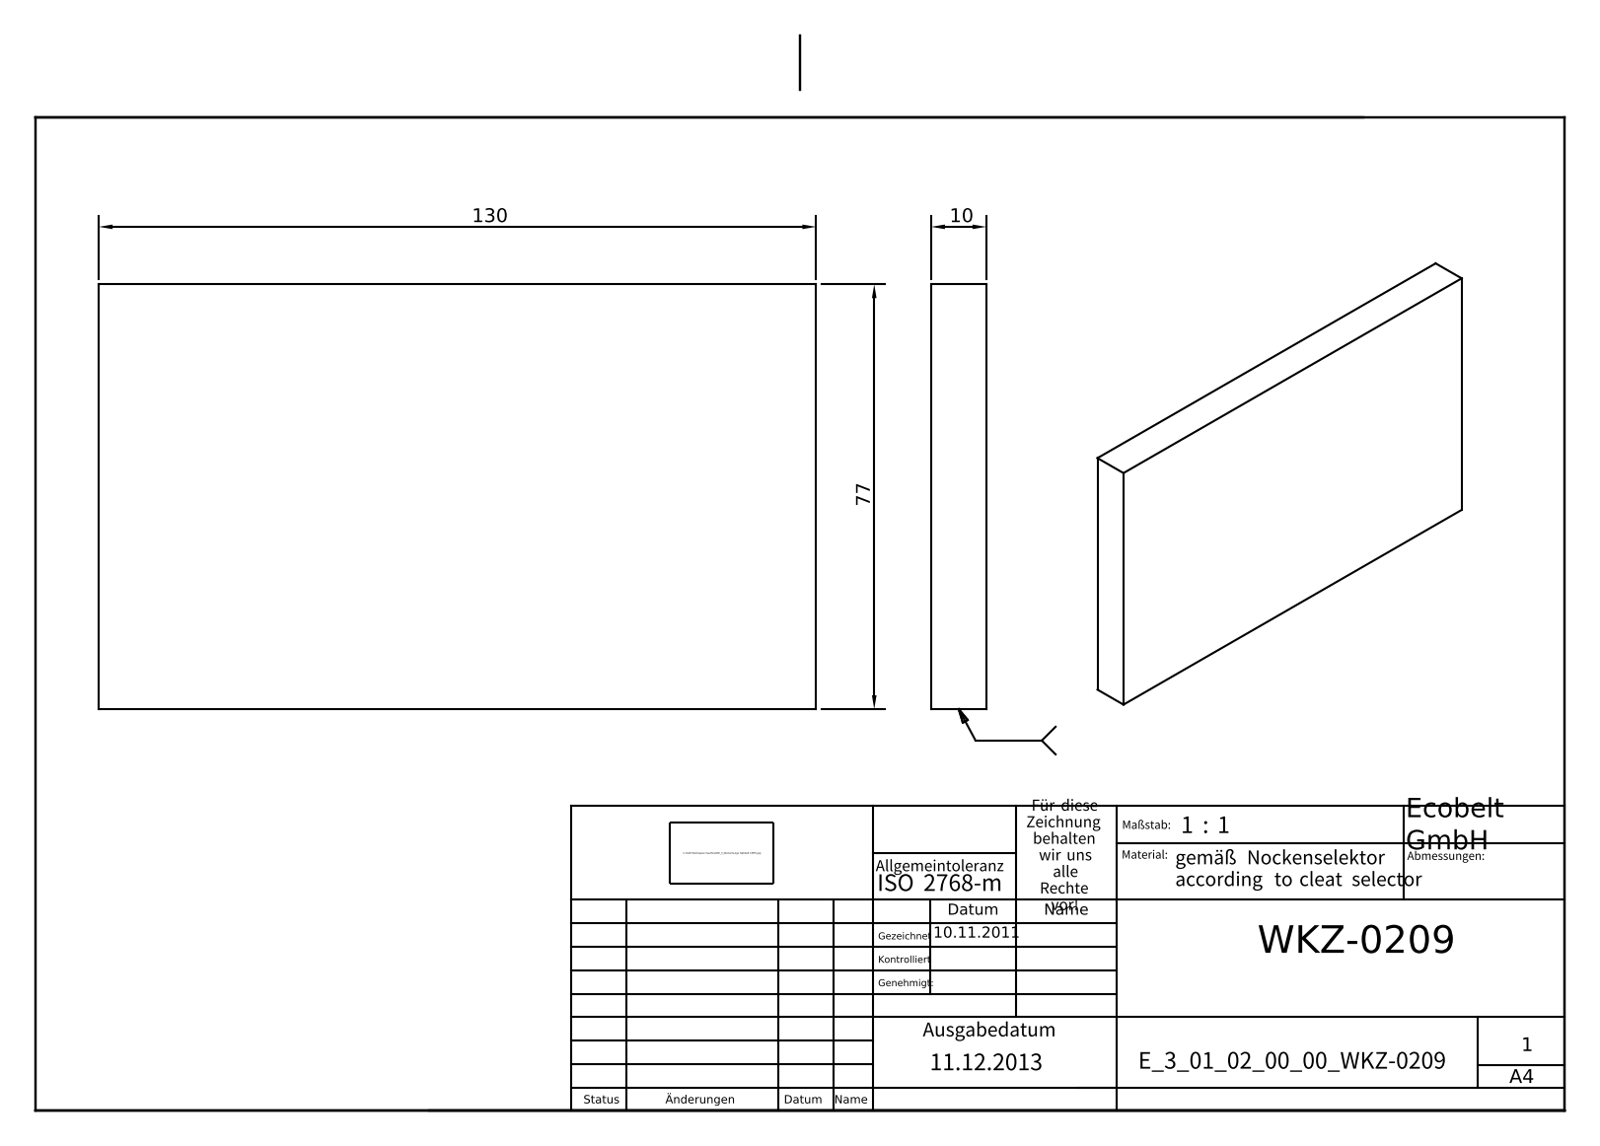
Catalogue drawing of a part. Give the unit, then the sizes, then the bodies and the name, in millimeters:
Units: millimetres
Overall size (bounding box): 130 × 77 × 10
Main face-to-face distances: 10, 77, 130
Volume: 100 100 mm³ · Surface area: 24 160 mm²
Bodies: 1 solid, 6 faces (6 planar, 0 cylindrical, 0 other)
Part name (STEP PRODUCT): E_3_01_02_00_00_WKZ-0209
STEP written by: Autodesk Inventor 2021 (AUTOMOTIVE_DESIGN)
